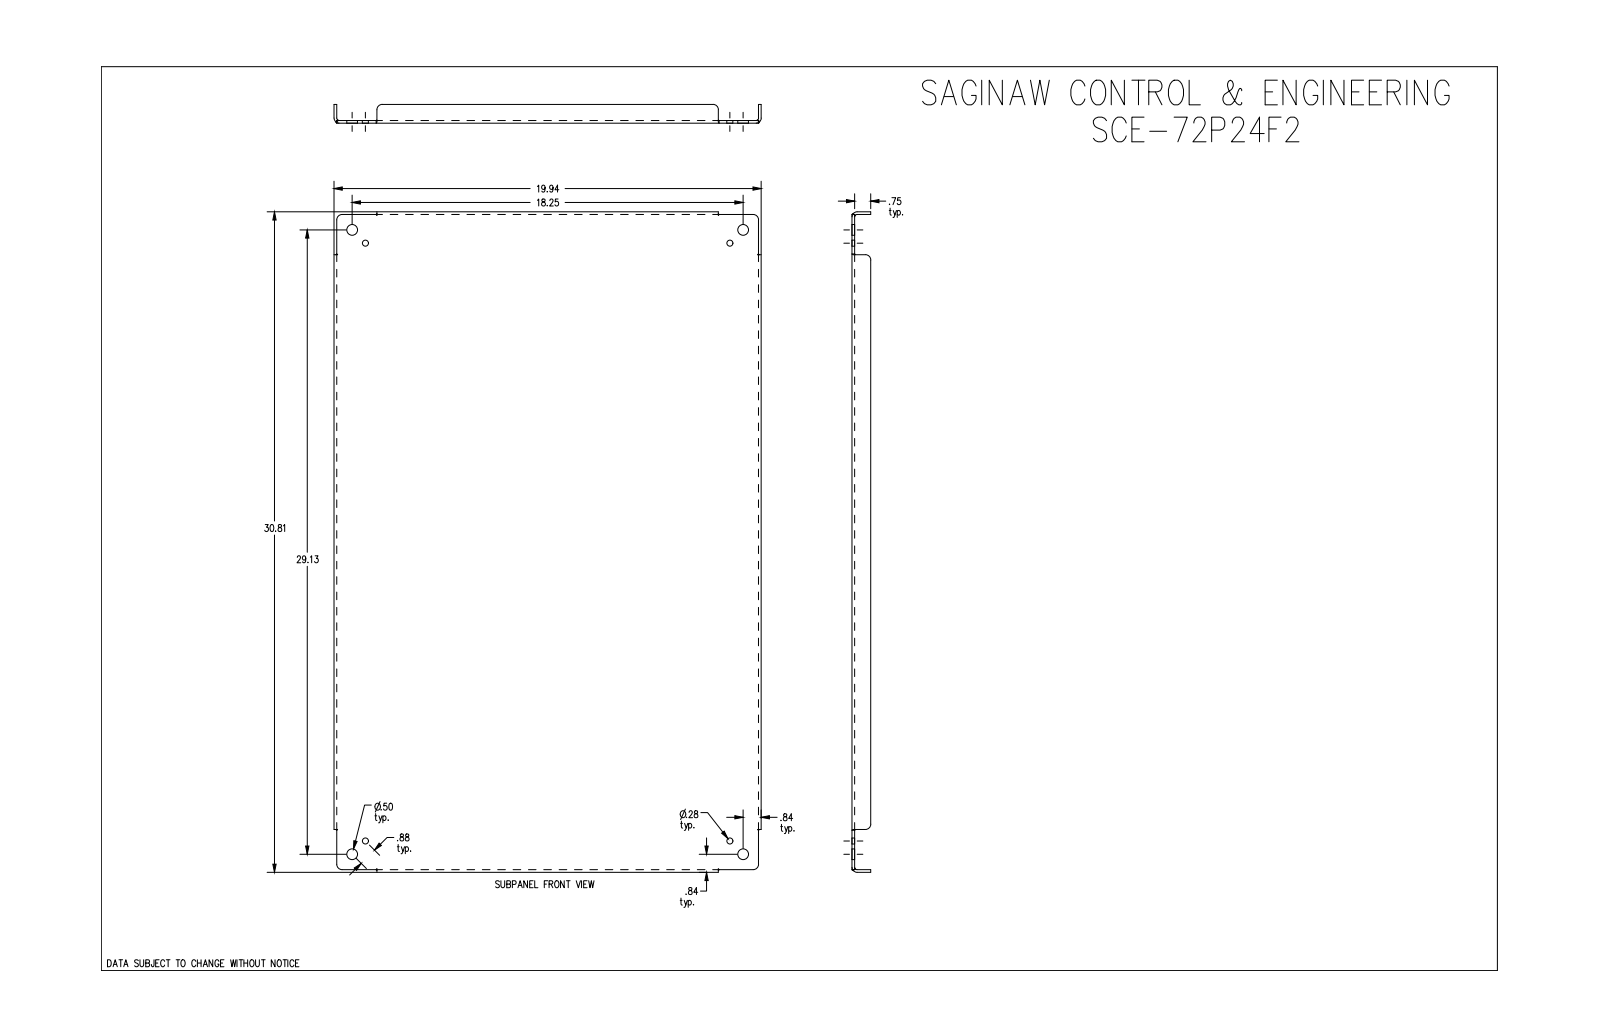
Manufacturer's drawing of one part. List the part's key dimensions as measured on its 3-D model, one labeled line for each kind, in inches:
Part name (STEP PRODUCT): SCE-72P24F2
STEP written by: SolidWorks 2019 (CONFIG_CONTROL_DESIGN)
Units: inches
Bodies: 1 solid, 82 faces (30 planar, 28 cylindrical, 24 other)
Overall size (bounding box): 30.813 × 19.938 × 0.875
Volume: 83.61 in³ · Surface area: 1 352 in²
Round holes (diameter × count): ⌀0.281 ×4, ⌀0.5 ×4
Partial cylindrical surfaces — rounded edges, fillets, slot ends (radius × count): R0.25 ×8, R0.112 ×4, R0.237 ×4
Main face-to-face distances: 0.125, 0.125, 19.813, 30.687, 19.687, 19.938, 30.562, 0.75, 0.875, 30.813
Hole centre spacings: 0.875, 17.642, 28.513, 33.518, 17.013, 18.25, 27.887, 29.125
